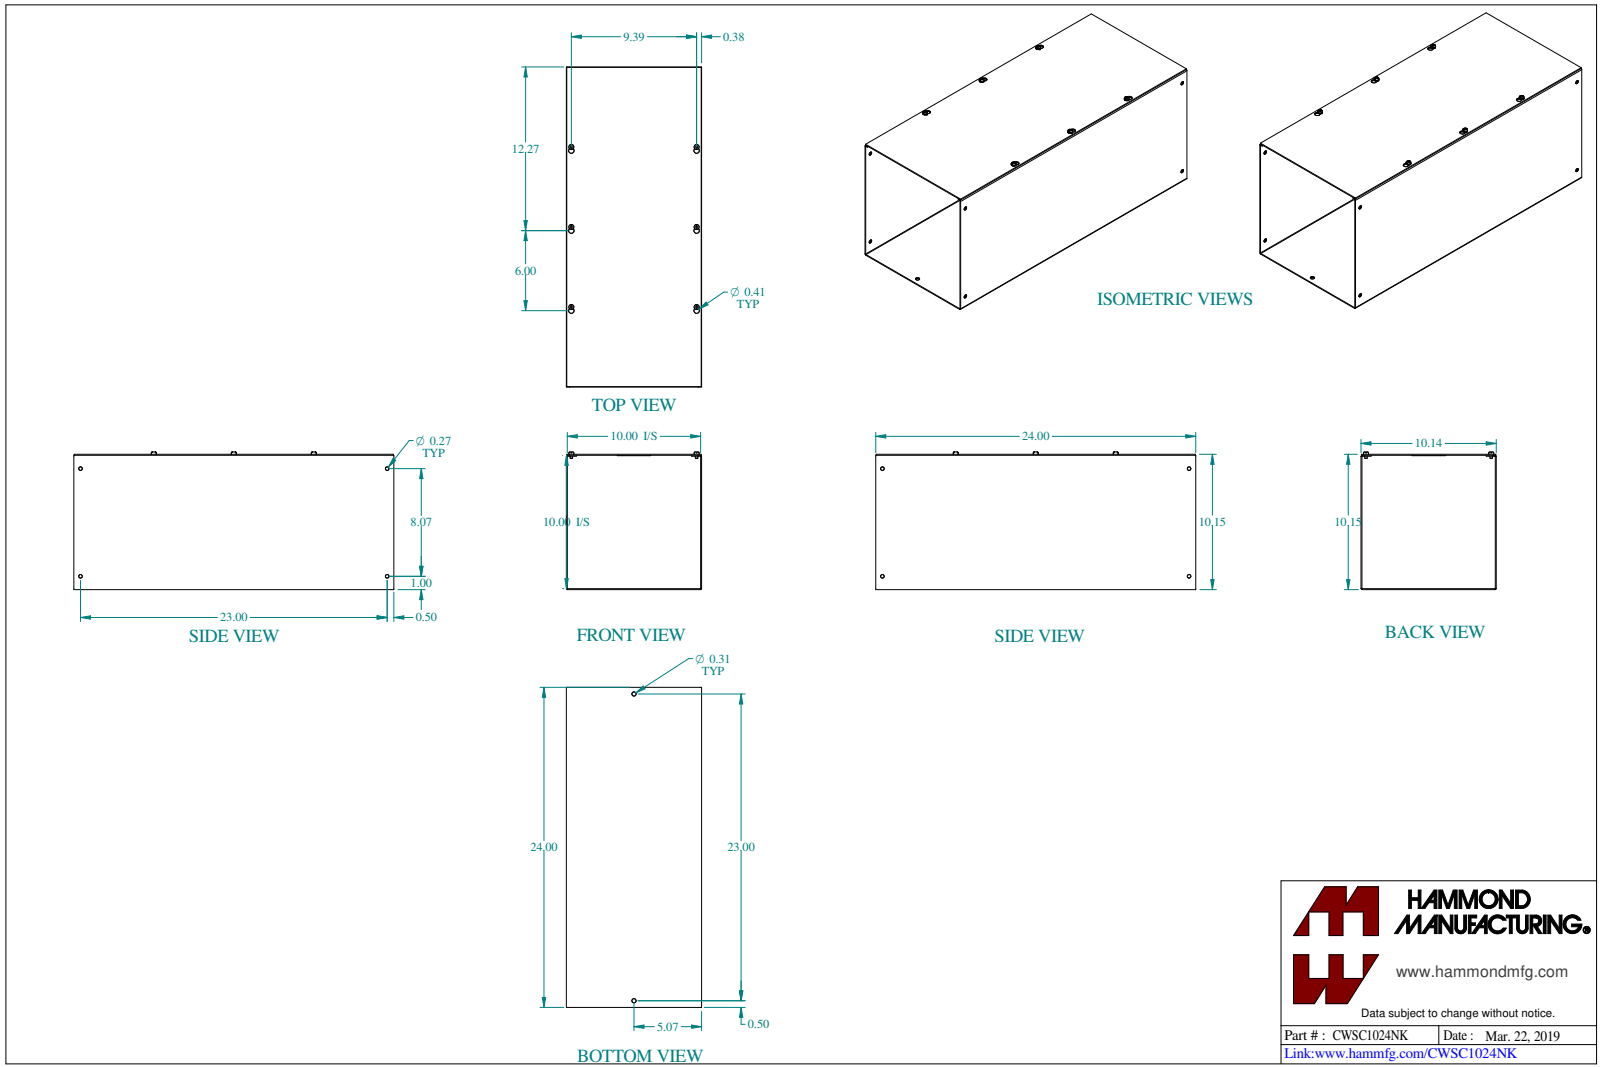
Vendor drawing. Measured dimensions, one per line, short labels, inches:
name: CWSC1024NK
written by: SolidWorks 2023 (CONFIG_CONTROL_DESIGN)
unit: in
bodies: 8 solids, 242 faces (118 planar, 88 cylindrical, 36 other)
size: 24 × 10.325 × 10.144
volume: 72.9 in³; area: 1 999 in²
holes: 6× ⌀0.177, 4× ⌀0.266, 2× ⌀0.313
bosses: 6× ⌀0.375, 6× ⌀0.19
rounds: 6× R0.125, 6× R0.203, 4× R0.036, 4× R0.108
face distances: 0.072, 10.072, 10, 0.078, 10.15, 10.078, 10.144, 9.928, 0.15, 0.031
hole spacings: 6, 7.233, 11.146, 12.422, 18.119, 9.394, 23, 8.072
